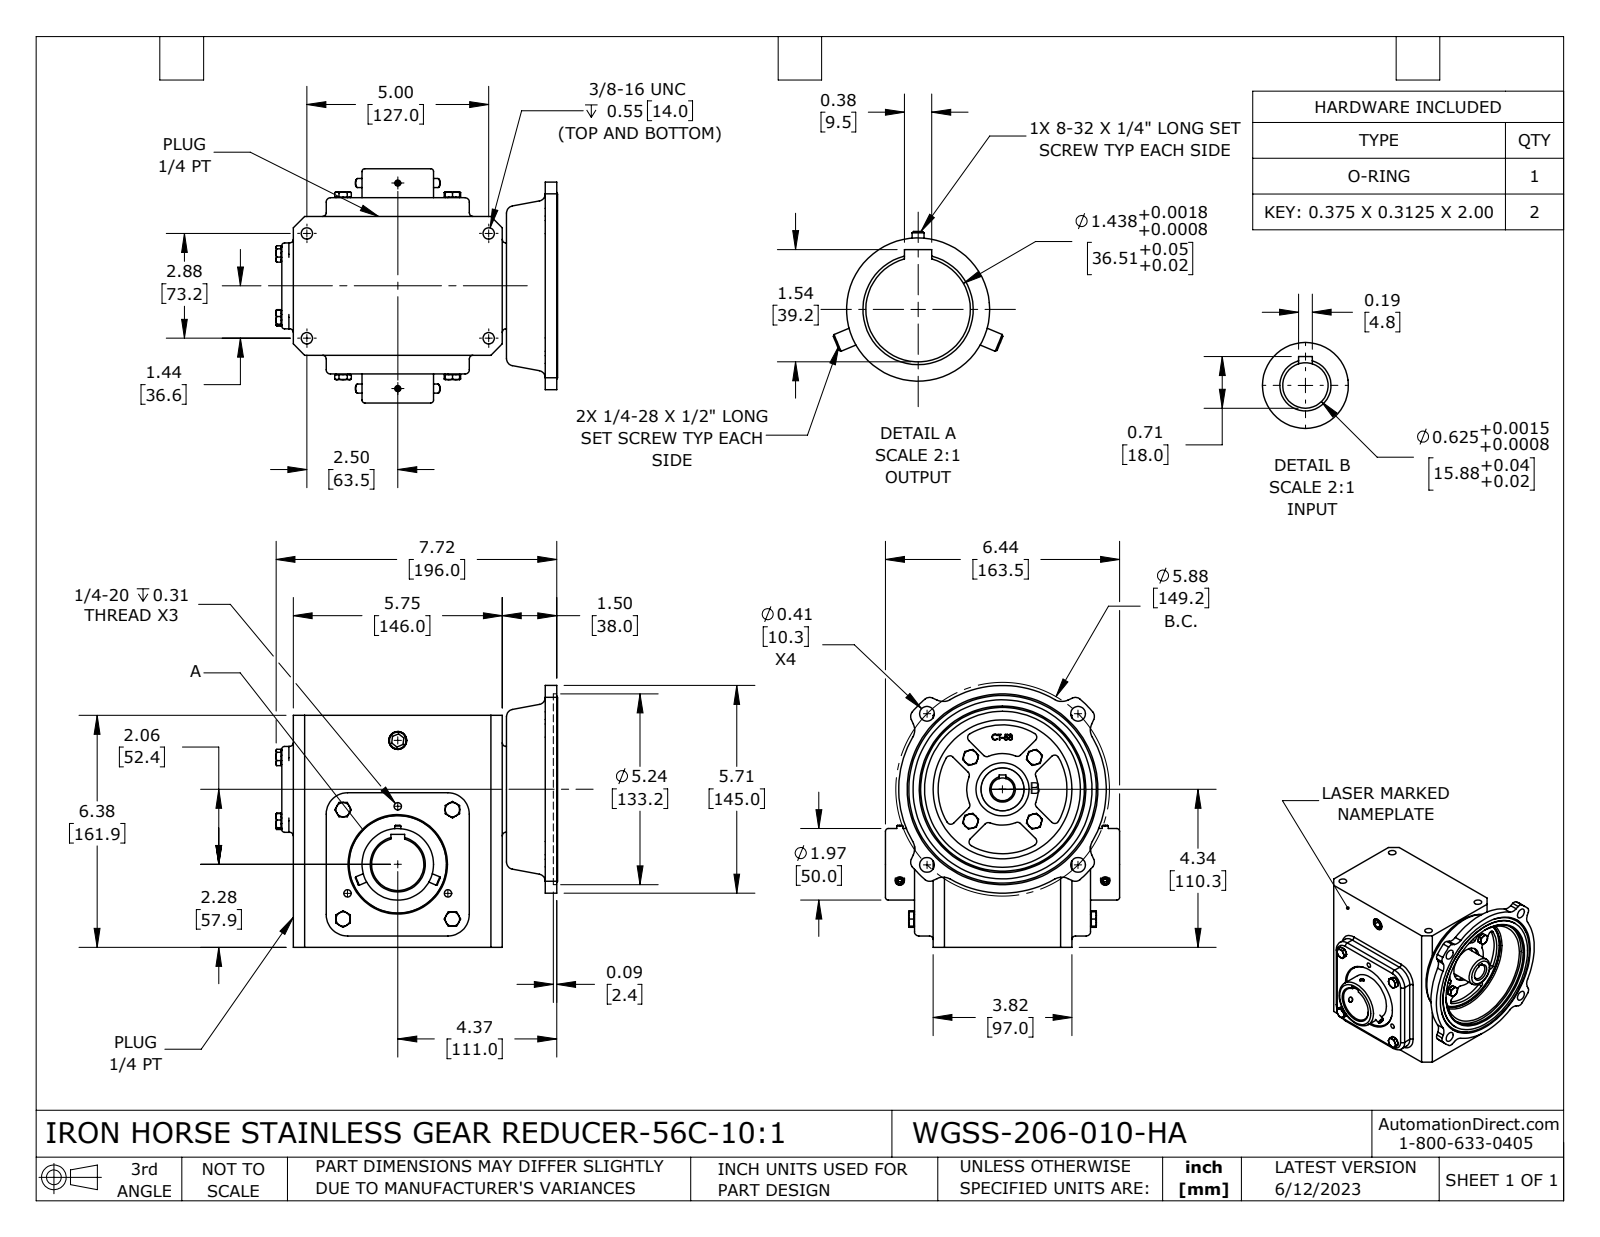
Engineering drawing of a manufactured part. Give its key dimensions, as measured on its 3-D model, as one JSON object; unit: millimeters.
{"part_name": "WGSS-206-010-HA", "step_written_by": "SolidWorks 2021 (CONFIG_CONTROL_DESIGN)", "units": "millimeters", "bodies": {"solids": 7, "faces": 895, "planar": 396, "cylindrical": 235, "other": 264}, "overall_size": [196.6, 182.8, 163.5], "volume_mm3": 2617000, "surface_area_mm2": 208800, "round_holes": [[5.4, 4], [8, 4], [10.3, 4], [5.1, 3], [3.5, 2], [15.9, 1], [22, 1], [36.5, 1], [36.6, 1], [37, 1], [40, 1], [97, 1]], "round_bosses_or_shafts": [[10, 8], [6.4, 4], [4.2, 2], [125, 1], [68, 1], [50, 1], [30, 1]], "partial_cylinders_radius": [[3, 24], [2.5, 16], [10, 12], [5, 8], [2, 4], [8, 4], [15, 4], [25, 1]], "face_to_face_distances": [161.9, 97, 13, 110, 146, 3, 8, 184, 123, 4], "hole_center_spacings": [72.6, 74.6, 105.5, 125.6, 40.5, 143.5, 70.2, 73.2]}
